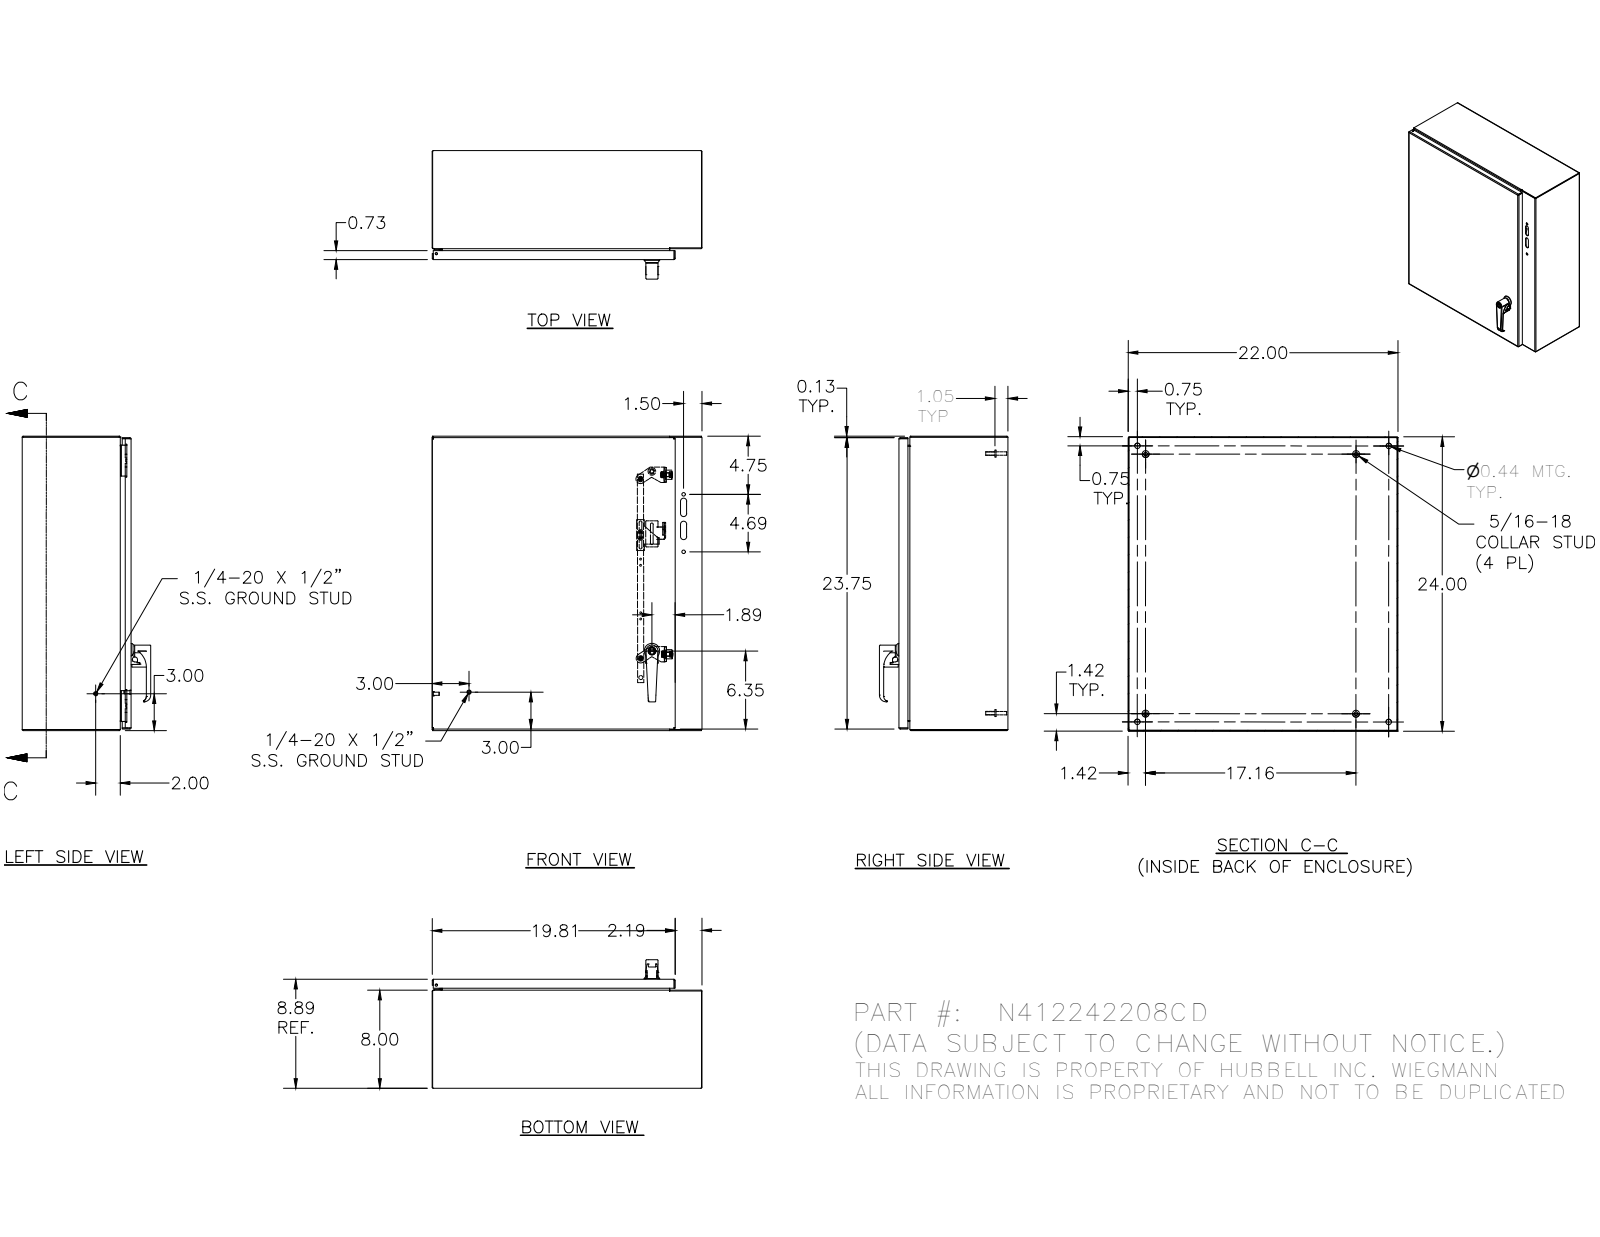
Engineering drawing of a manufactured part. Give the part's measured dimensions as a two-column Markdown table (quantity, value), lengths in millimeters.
| quantity | value |
| --- | --- |
| part name | N412242208CD |
| STEP written by | SolidWorks 2019 (AUTOMOTIVE_DESIGN) |
| units | millimeters |
| bodies | 60 solids, 2070 faces (810 planar, 743 cylindrical, 517 other) |
| overall size | 609.6 × 558.8 × 267 |
| volume | 2 479 000 mm³ |
| surface area | 2 610 000 mm² |
| round holes (diameter × count) | 3.7 × 6, 2.4 × 4, 3.9 × 4, 4 × 4, 4.2 × 4, 4.4 × 4, 4.7 × 4, 11.1 × 4, 8.1 × 3, 5 × 2, 5.4 × 2, 5.6 × 2 |
| round bosses / shafts (diameter × count) | 6.4 × 12, 7.6 × 8, 14.3 × 4, 11.1 × 4, 9.1 × 4, 8.1 × 4, 7 × 4, 6.5 × 4 |
| partial cylindrical surfaces (radius × count) | 0.5 × 38, 0.3 × 31, 1.3 × 26, 3.2 × 25, 0.4 × 18, 0.4 × 16, 0.6 × 16, 2.3 × 16 |
| main face-to-face distances | 1.9, 224.6, 222.7, 226.5, 556.9, 607.7, 23.3, 201.3, 555, 558.8 |
| hole center spacings | 508, 12.7, 530.1, 16.7, 16.8, 25, 33.2, 33.3 |
